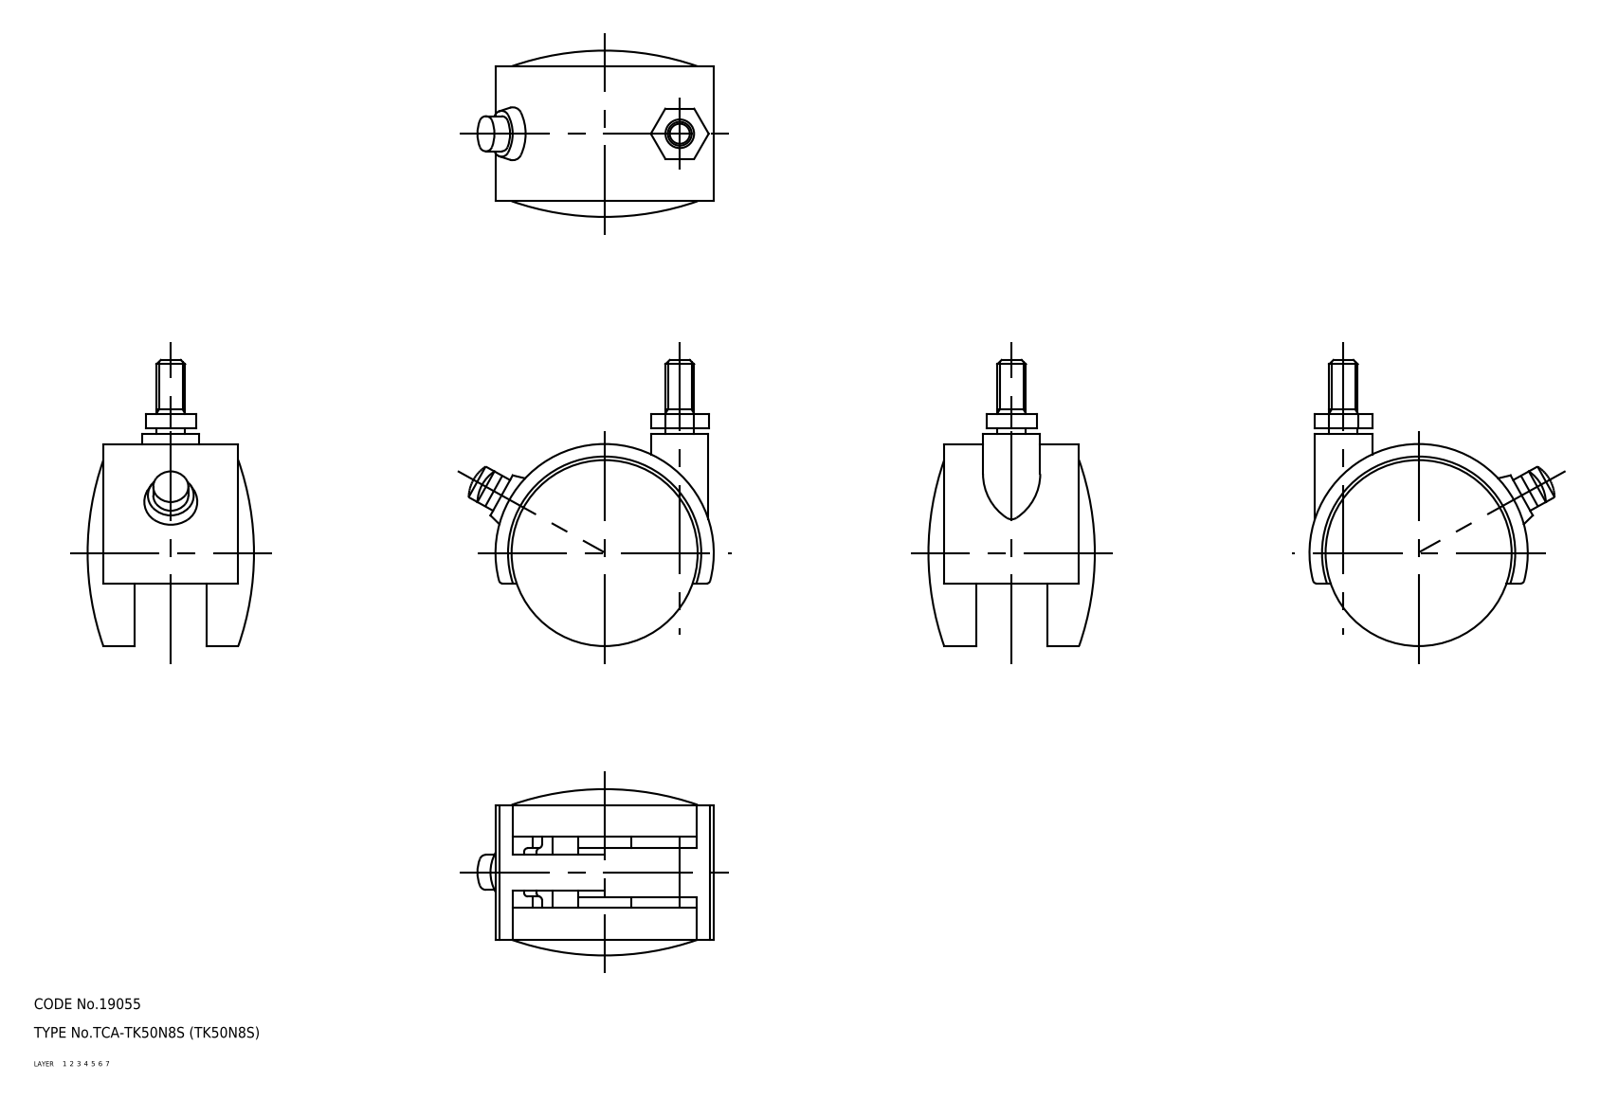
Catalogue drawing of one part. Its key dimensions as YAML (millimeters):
part_name: "wheel; main shaft; TK50N8S_4882_36"
step_written_by: "CADfix (AUTOMOTIVE_DESIGN)"
units: millimeters
bodies: {solids: 4, faces: 100, planar: 0, cylindrical: 0, other: 100}
overall_size: [80, 66.05, 46.5]
volume: 68877
surface_area: 30104
